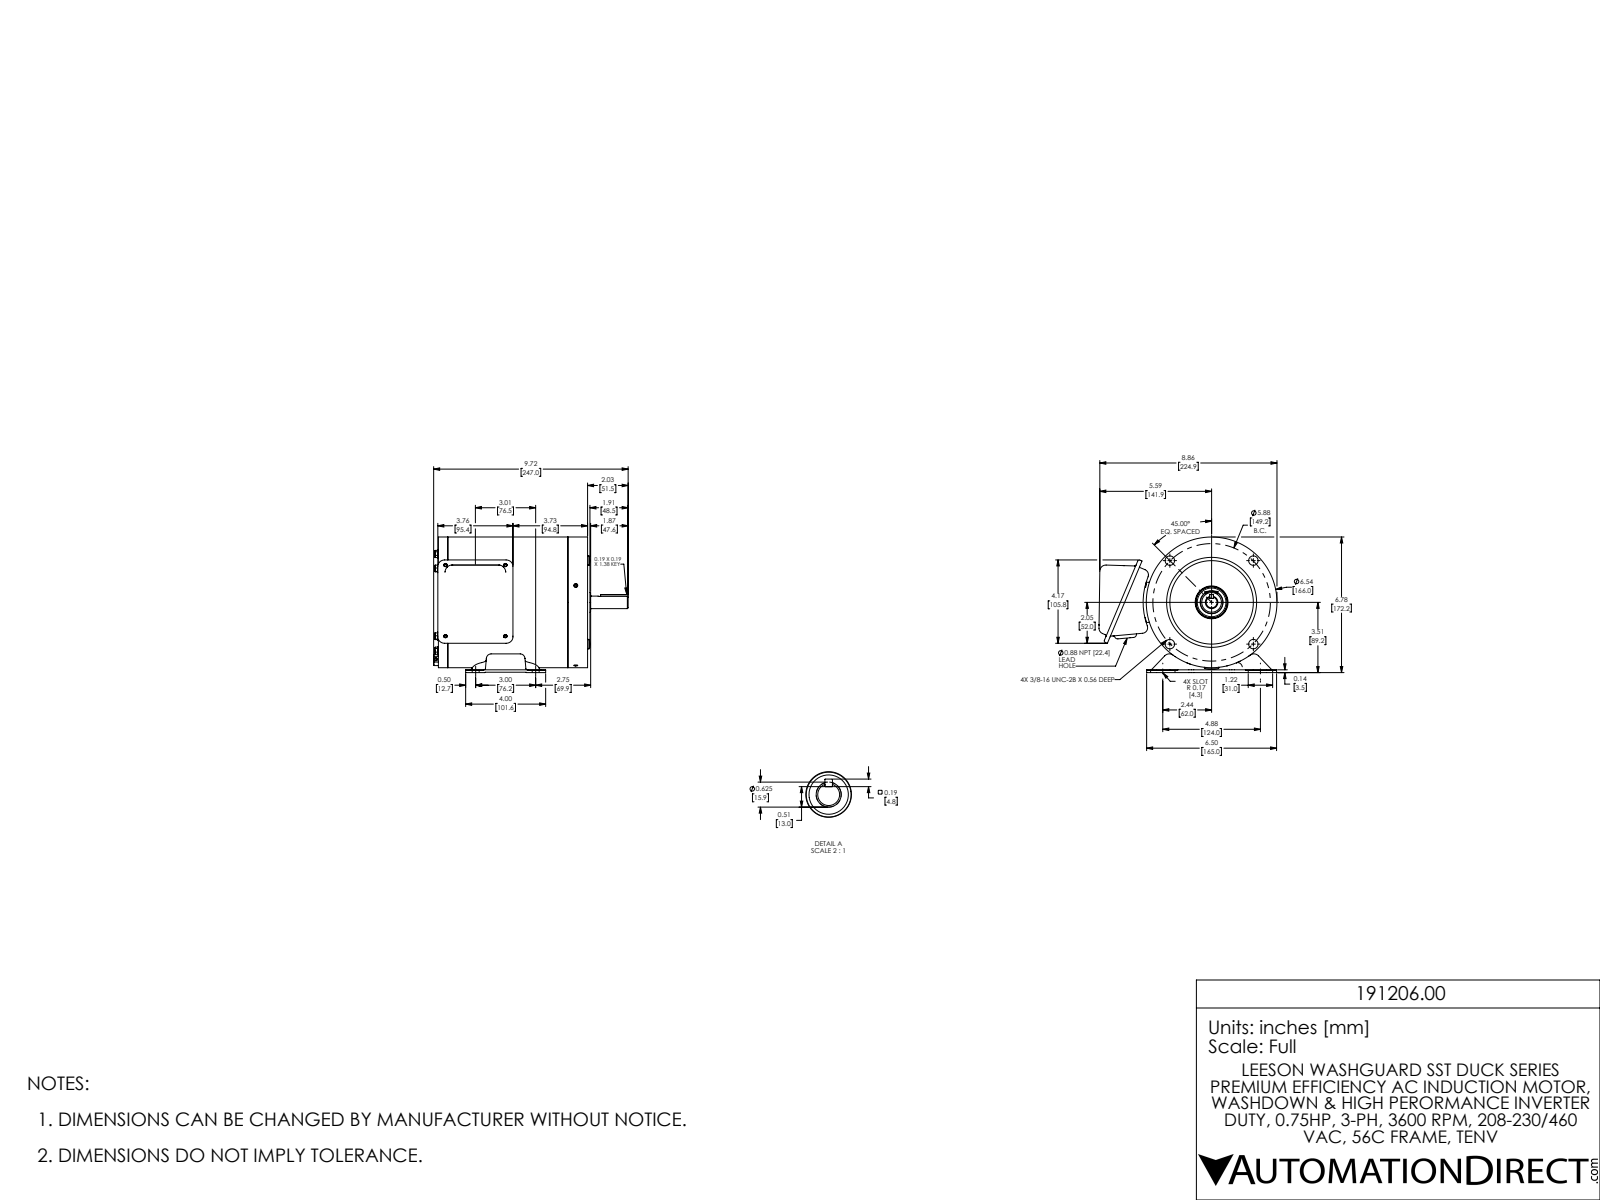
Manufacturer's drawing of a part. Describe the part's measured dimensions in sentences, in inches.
The part is named "191207". Its 3-D file was written by "SolidWorks 2017 (AUTOMOTIVE_DESIGN)". It is 27 solids with 1155 faces: 238 planar, 458 cylindrical and 459 other. Overall it measures 9.724 by 8.898 by 6.78 inches. Its volume is 48.33 cubic inches and its surface area 740.3 square inches. Round holes: 15 of diameter 0.197, 9 of diameter 0.13, 9 of diameter 0.138, 8 of diameter 0.165, 8 of diameter 0.268, 6 of diameter 0.177, 4 of diameter 0.228, 2 of diameter 0.118, 2 of diameter 0.157, 1 of diameter 0.189, 1 of diameter 0.63, 1 of diameter 0.866. Round bosses or shafts: 4 of diameter 0.472, 4 of diameter 0.413, 4 of diameter 0.319, 4 of diameter 0.197, 1 of diameter 6.535, 1 of diameter 4.5, 1 of diameter 2.362, 1 of diameter 1.575. Partial cylindrical surfaces (rounded edges, fillets, slot ends): 44 of radius 0.079, 16 of radius 0.157, 15 of radius 0.236, 14 of radius 0.02, 11 of radius 0.276, 9 of radius 0.303, 8 of radius 0.039, 8 of radius 0.173. The main face-to-face distances are 0.039, 0.217, 0.118, 0.197, 7.461, 7.244, 0.236, 0.394, 7.047, 7.224. The hole center spacings are 1.496, 2.231, 2.953, 5.383, 0.236, 2.992, 0.394, 0.515.
